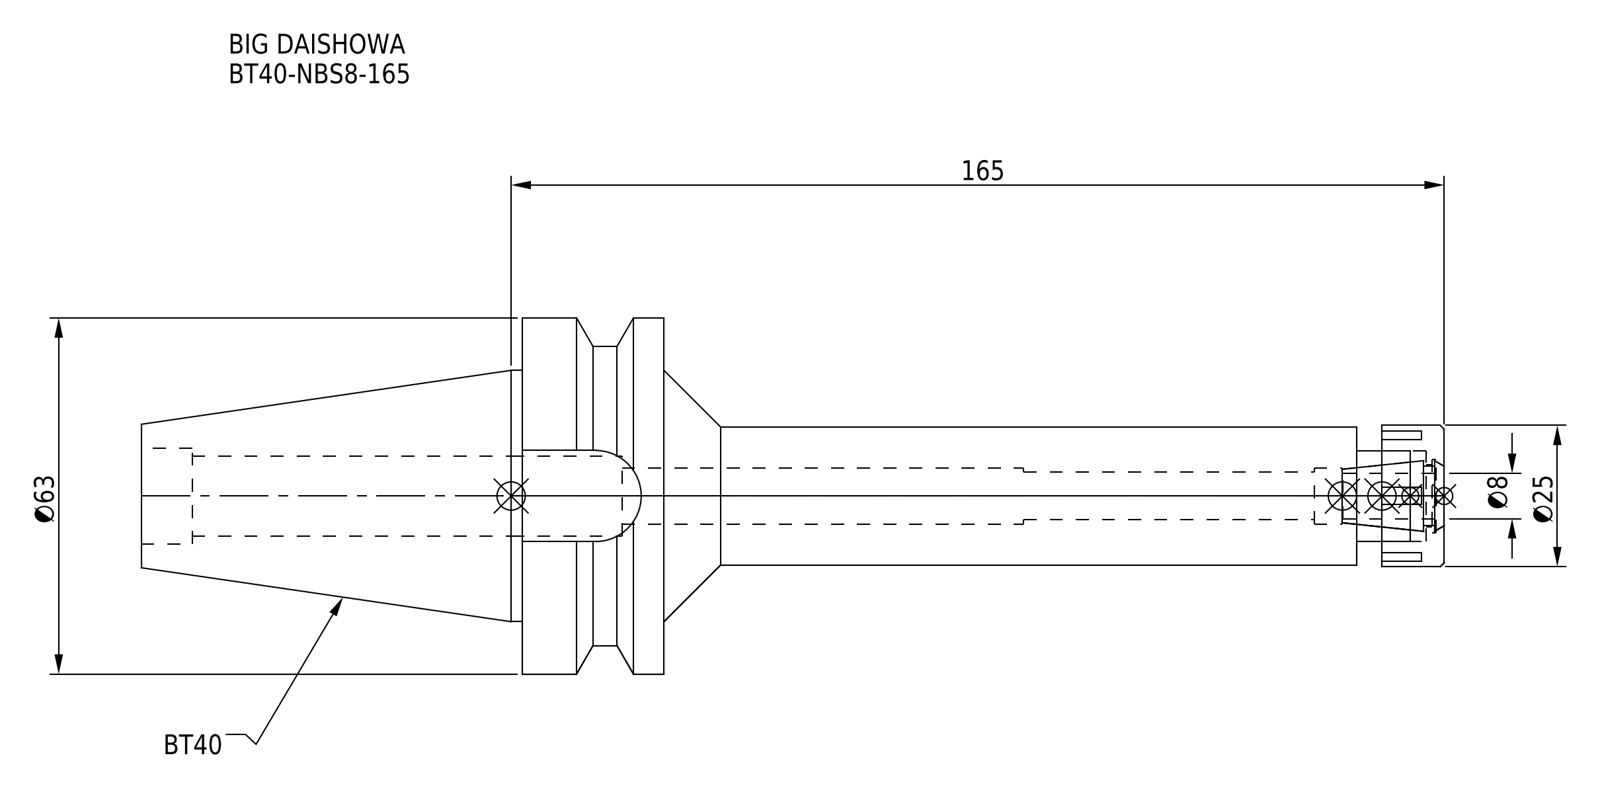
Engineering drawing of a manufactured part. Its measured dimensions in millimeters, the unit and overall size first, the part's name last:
Units: millimetres
Overall size (bounding box): 230.4 × 63 × 63
Round holes (diameter × count): ⌀8.4 ×1, ⌀10 ×1, ⌀11 ×1, ⌀13 ×1, ⌀14.2 ×1, ⌀16 ×1, ⌀17 ×1
Round bosses / shafts (diameter × count): ⌀63 ×1, ⌀53 ×1, ⌀44.45 ×1, ⌀25 ×1, ⌀24.5 ×1
Partial cylindrical surfaces — rounded edges, fillets, slot ends (radius × count): R8.05 ×1
Main face-to-face distances: 25, 138, 163, 45, 230.4, 92.4, 67.4, 15.5, 122.5, 147.5
Volume: 178 146 mm³ · Surface area: 38 514 mm²
Bodies: 2 solids, 93 faces (45 planar, 34 cylindrical, 14 other)
Part name (STEP PRODUCT): BT40-NBS8-165-FreeParts; NBN8_1.stp; BT40-NBS8-165.stp; DXF_TEMP_ASSY_ASM_4_ASM.stp (+3 more)
STEP written by: SolidWorks 2019 (CONFIG_CONTROL_DESIGN)
